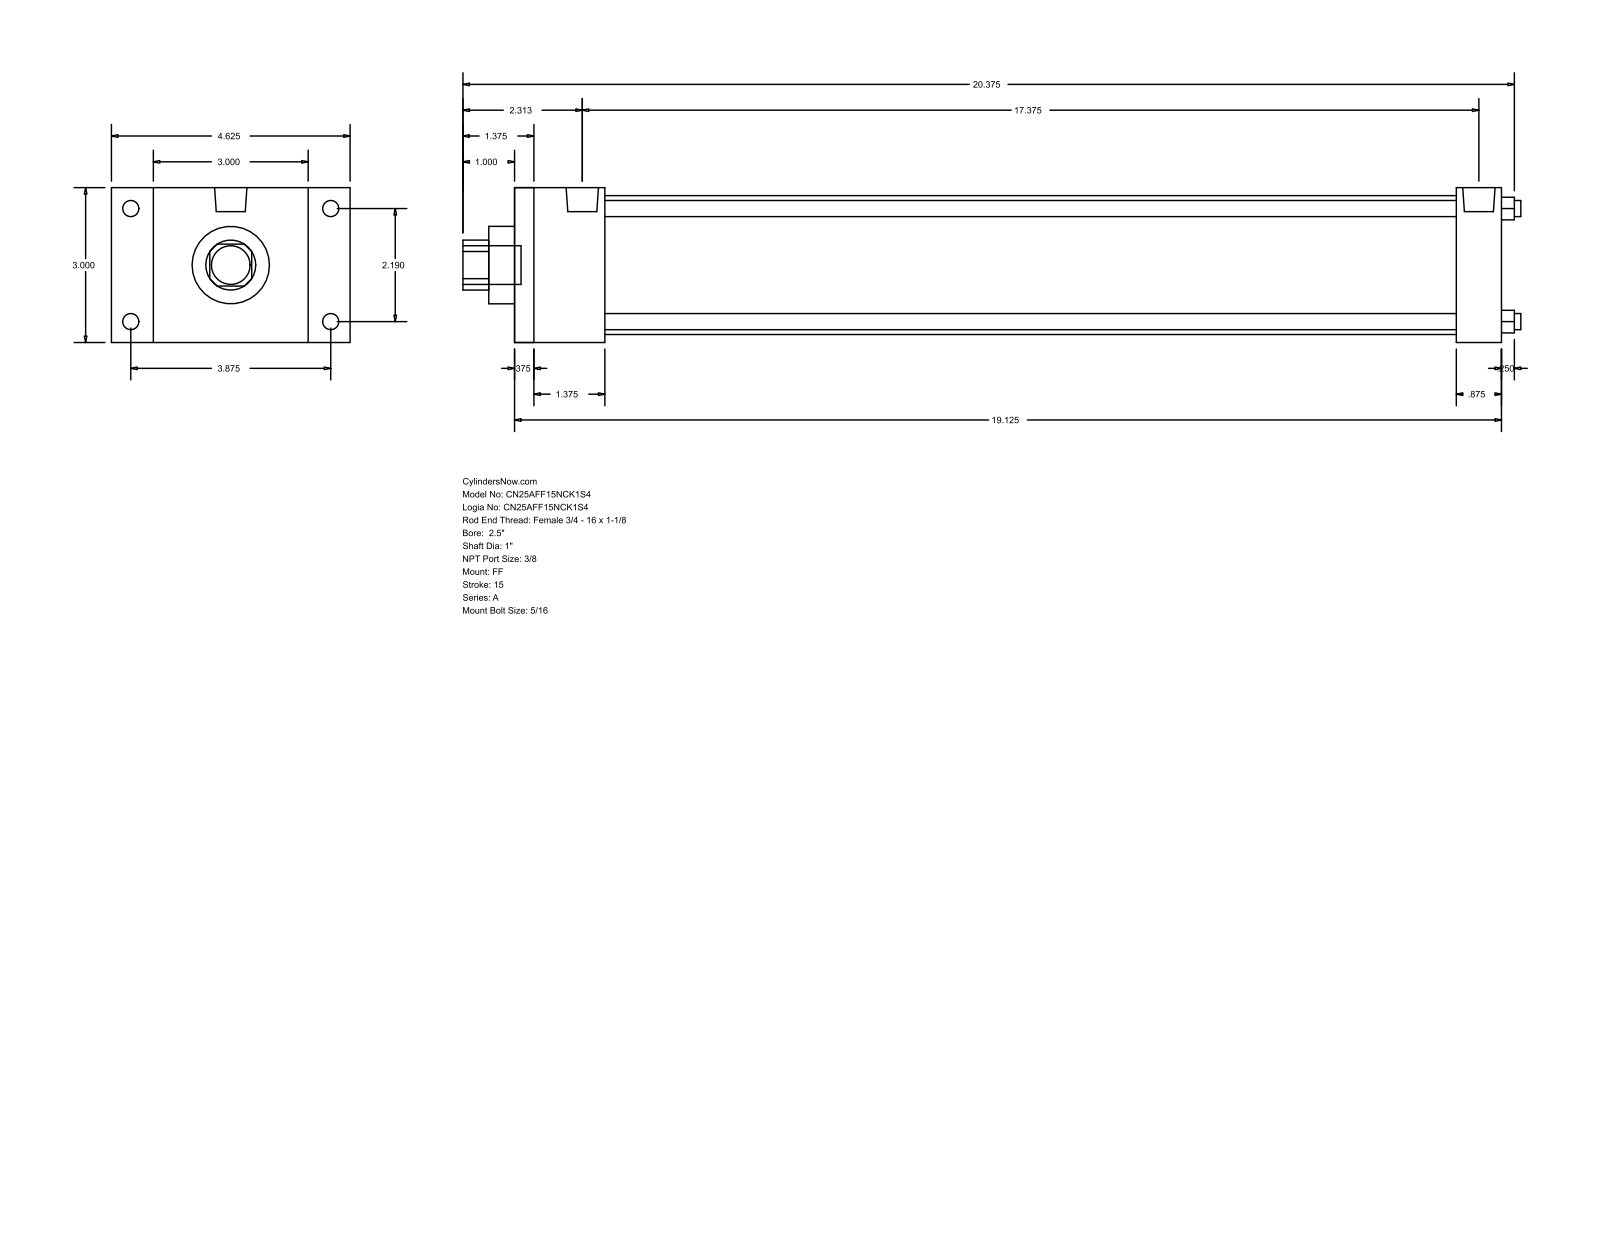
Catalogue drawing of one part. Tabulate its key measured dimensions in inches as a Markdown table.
| quantity | value |
| --- | --- |
| part name | A_FF__0250_1 |
| STEP written by | GSSL Pune (CONFIG_CONTROL_DESIGN) |
| units | inches |
| bodies | 0 solids, 92 faces (64 planar, 28 cylindrical, 0 other) |
| overall size | 20.5 × 4.625 × 3 |
| round holes (diameter × count) | 0.313 × 4, 1 × 1, 1.5 × 1, 2.69 × 1 |
| round bosses / shafts (diameter × count) | 0.313 × 4, 0.219 × 4, 0.627 × 2, 0.75 × 1 |
| partial cylindrical surfaces (radius × count) | 0.484 × 1 |
| main face-to-face distances | 3, 19.125, 0.375, 18.75, 1.75, 18.25, 1.375, 17.875, 16.5, 17.375 |
| hole center spacings | 1.548, 2.19, 3.097 |
